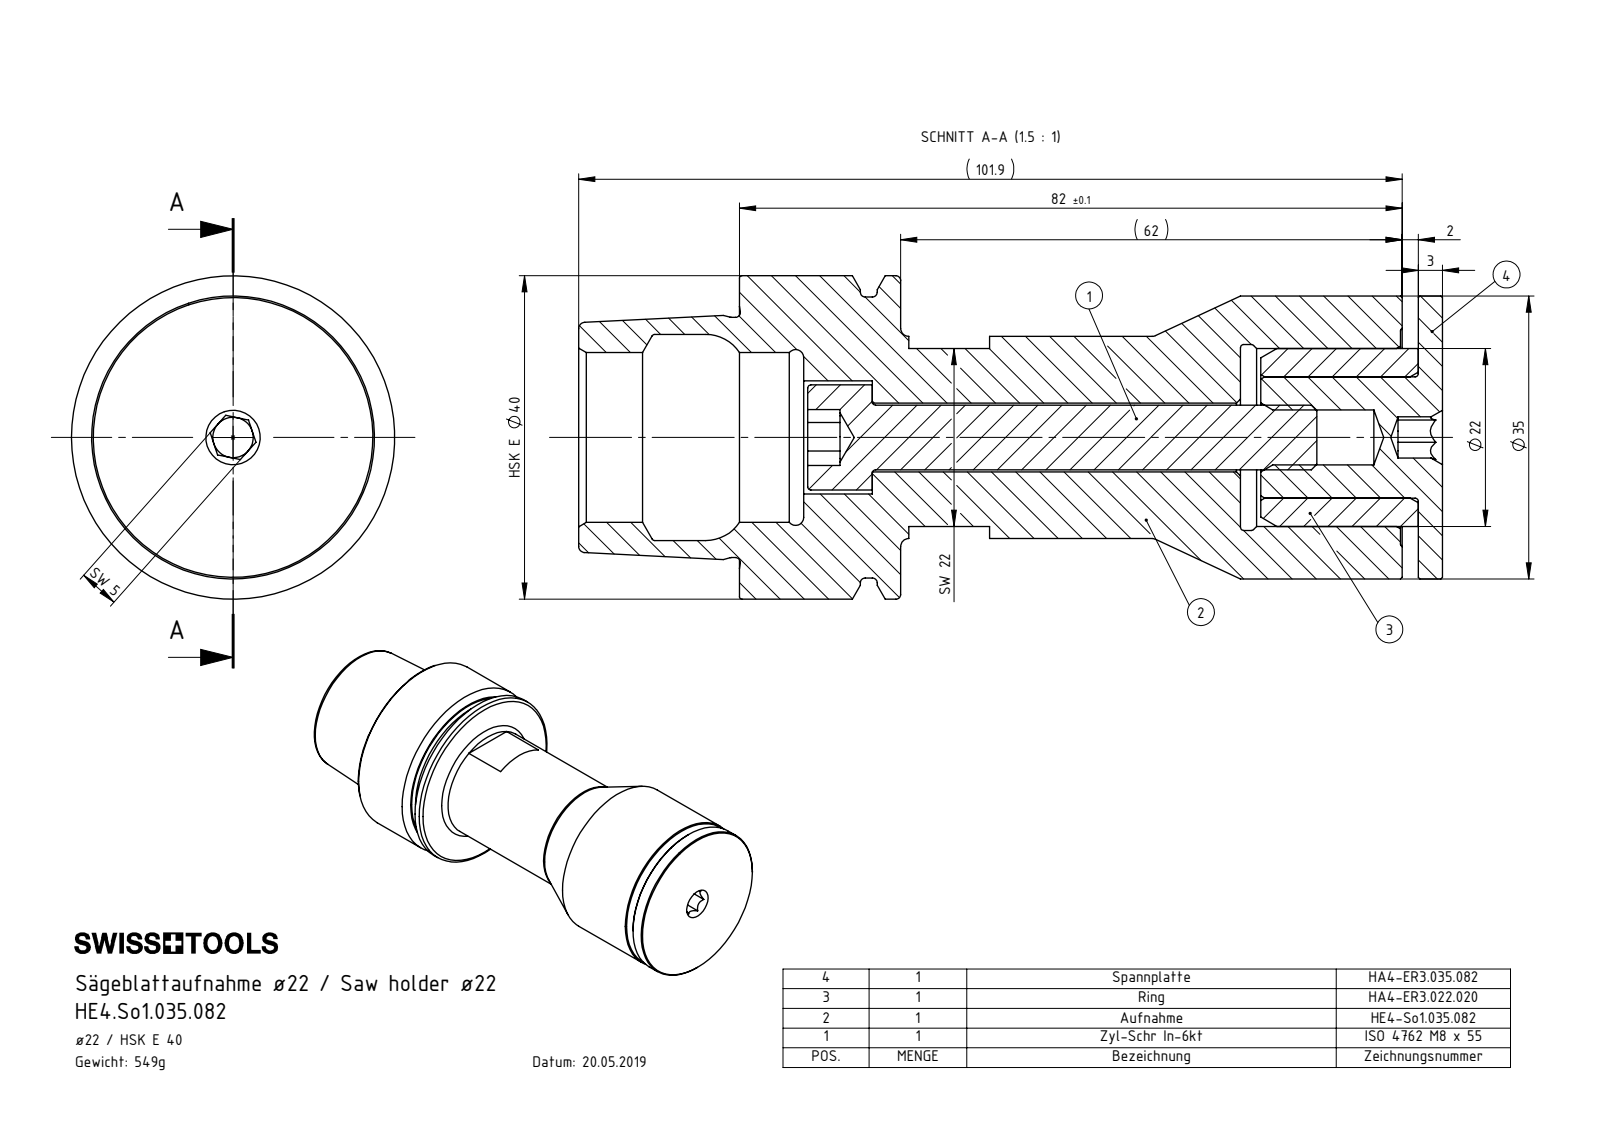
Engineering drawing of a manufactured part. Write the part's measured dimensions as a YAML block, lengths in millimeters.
part_name: "HE4.So1.035.082; HE4-So1.035.082_A_Fertigbearbeitung; ISO 4762 - M8 x 55_PreviewCfg; HA4-ER3.022.020_A (+1 more)"
step_written_by: "SolidWorks 2017 (AUTOMOTIVE_DESIGN)"
units: millimeters
bodies: {solids: 4, faces: 111, planar: 48, cylindrical: 20, other: 43}
overall_size: [106.9, 40, 40]
volume: 69998
surface_area: 26399
round_holes:
  - {diameter: 6.8, count: 1}
  - {diameter: 8.5, count: 1}
  - {diameter: 14, count: 1}
  - {diameter: 15, count: 1}
  - {diameter: 21, count: 1}
  - {diameter: 22, count: 1}
  - {diameter: 23, count: 1}
  - {diameter: 25.5, count: 1}
round_bosses_or_shafts:
  - {diameter: 40, count: 1}
  - {diameter: 35, count: 1}
  - {diameter: 34.75, count: 1}
  - {diameter: 29.71, count: 1}
  - {diameter: 25, count: 1}
  - {diameter: 13, count: 1}
  - {diameter: 8, count: 1}
face_to_face_distances: [3, 64.05, 67.05, 22, 5, 19.95, 84, 87, 82, 62.05]
